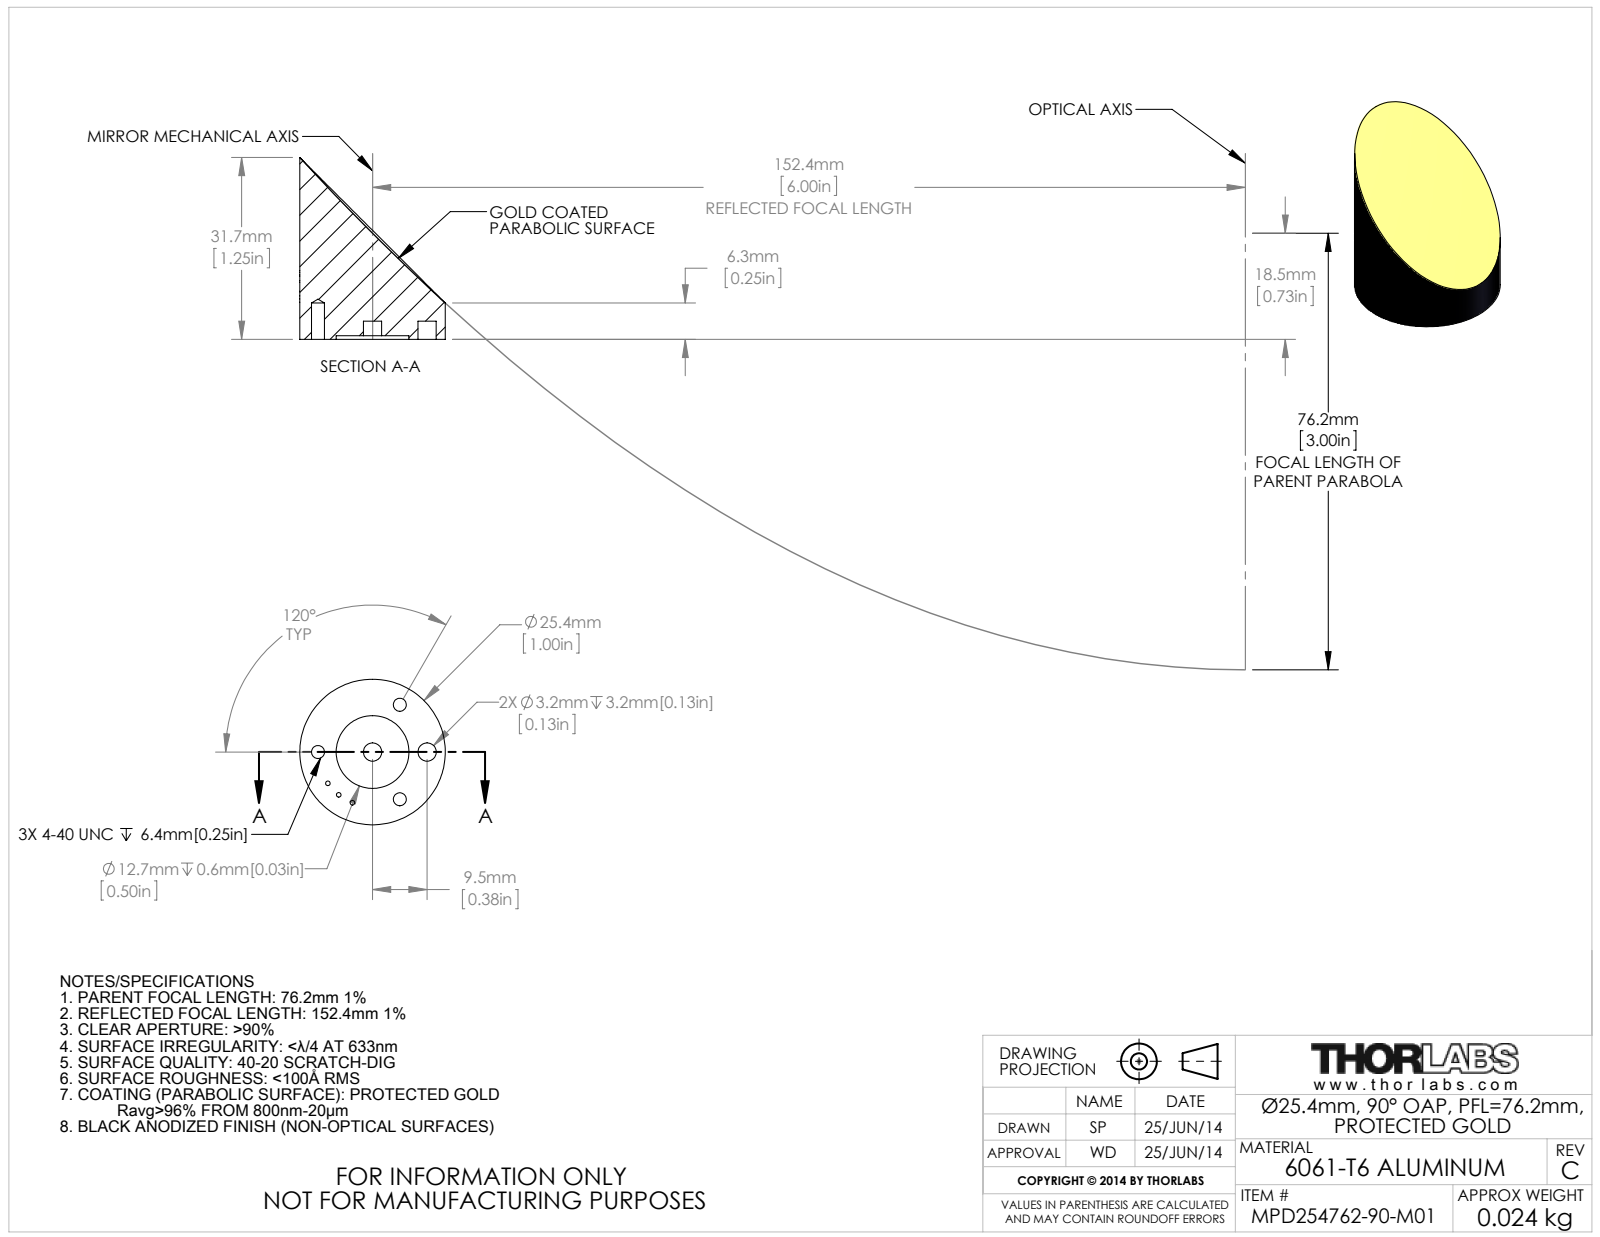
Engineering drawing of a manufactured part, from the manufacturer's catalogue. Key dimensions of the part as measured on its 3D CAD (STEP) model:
Part name (STEP PRODUCT): 21175-E0W
STEP written by: SolidWorks 2014 (CONFIG_CONTROL_DESIGN)
Units: inches
Bodies: 1 solid, 68 faces (4 planar, 50 cylindrical, 14 other)
Overall size (bounding box): 1.25 × 1 × 1
Volume: 0.568 in³ · Surface area: 4.595 in²
Round holes (diameter × count): ⌀0.089 ×3, ⌀0.126 ×2, ⌀0.5 ×1
Round bosses / shafts (diameter × count): ⌀1 ×1
Main face-to-face distances: 0.025, 0.125, 0.1
Hole centre spacings: 0.375, 0.375, 0.65, 0.75
